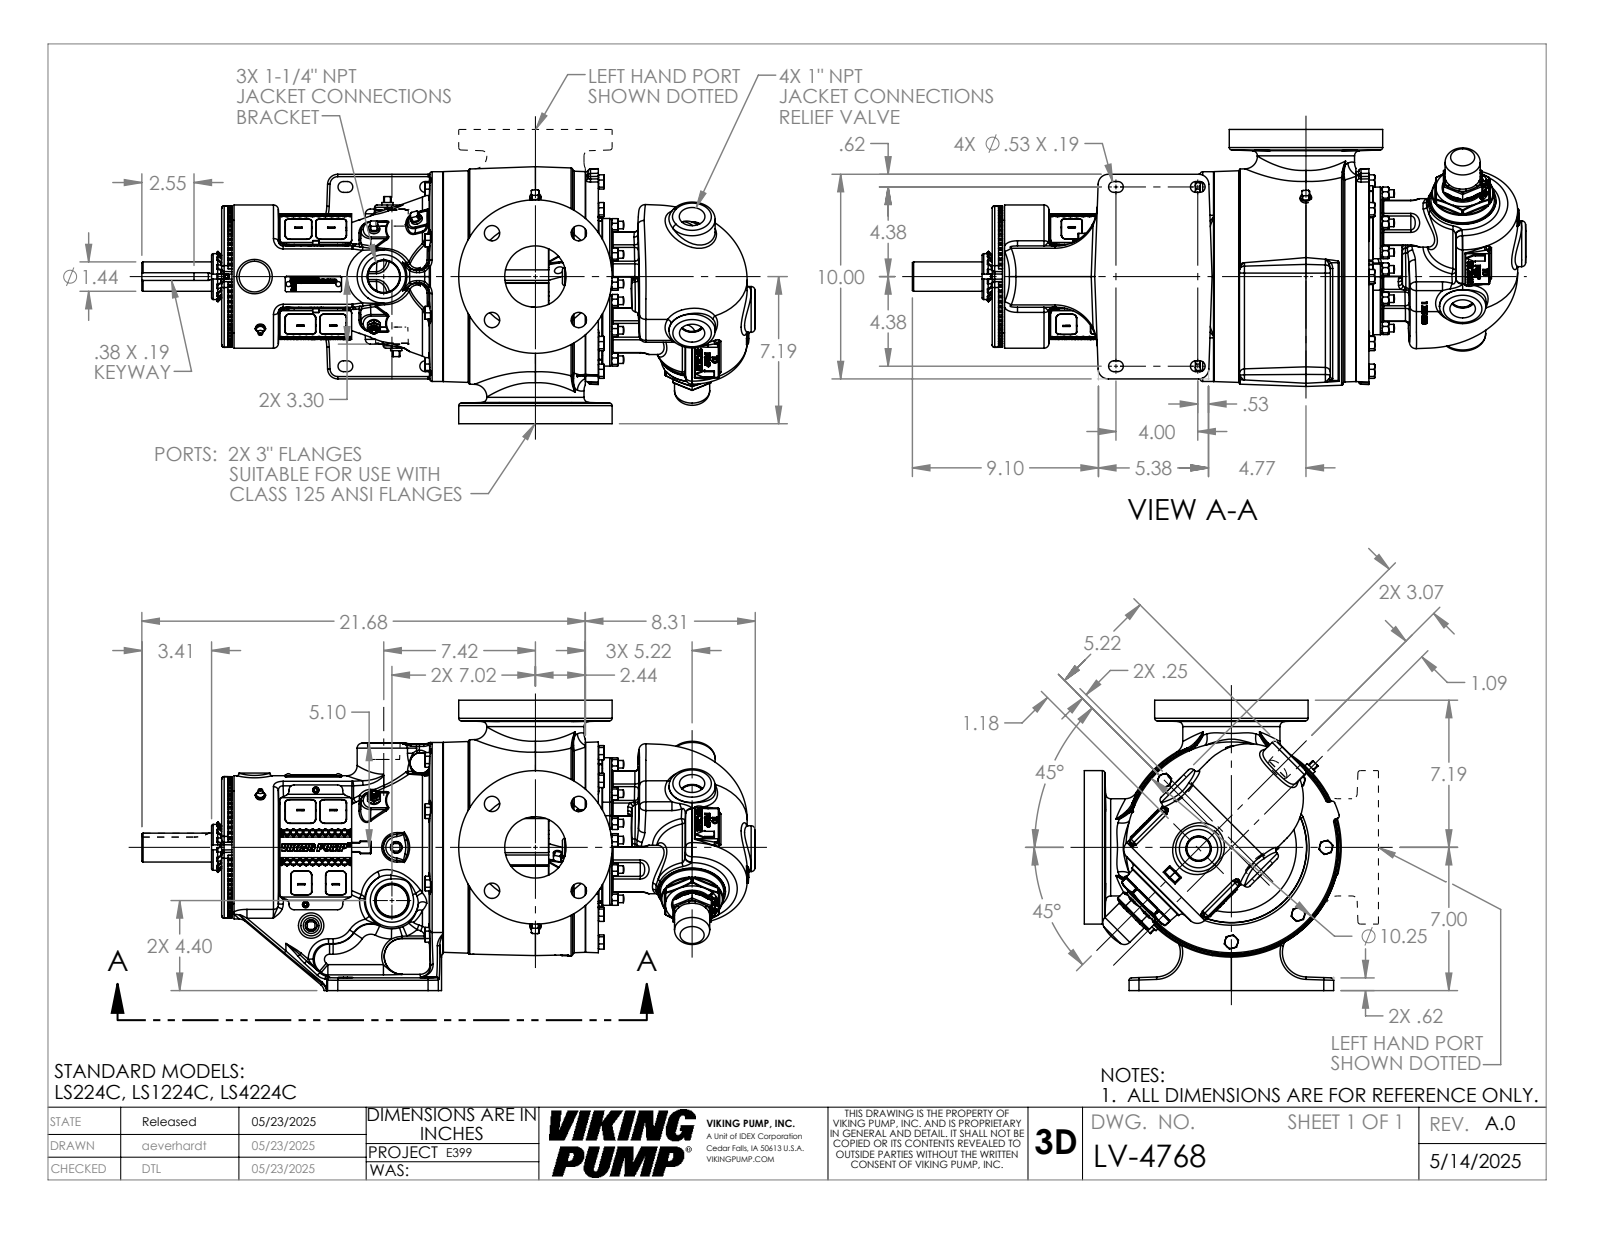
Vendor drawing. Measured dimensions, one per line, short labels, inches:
name: LV-4768
written by: SolidWorks 2024 (AUTOMOTIVE_DESIGN)
unit: in
bodies: 1 solid, 5285 faces (1672 planar, 875 cylindrical, 2738 other)
size: 29.989 × 14.19 × 12.56
volume: 1 351 in³; area: 1 656 in²
holes: 8× ⌀0.75, 8× ⌀1.094, 6× ⌀0.199, 6× ⌀0.25, 3× ⌀0.159, 2× ⌀0.266, 2× ⌀0.313, 1× ⌀0.2, 1× ⌀0.453, 1× ⌀1.506, 1× ⌀1.577, 1× ⌀1.593
bosses: 10× ⌀0.625, 8× ⌀0.369, 6× ⌀0.625, 3× ⌀3.5, 3× ⌀0.437, 3× ⌀0.312, 2× ⌀7.5, 2× ⌀4.75
rounds: 109× R0.063, 80× R0.12, 74× R0.069, 36× R0.03, 36× R0.5, 16× R0.24, 14× R0.19, 12× R0.25
face distances: 14.19, 1.5, 2.25, 0.5, 12.13, 3.534, 15.664, 2.146, 5.68, 17.81
hole spacings: 3, 4.243, 1.375, 2.18, 3.609, 4.446, 4.625, 6.404
